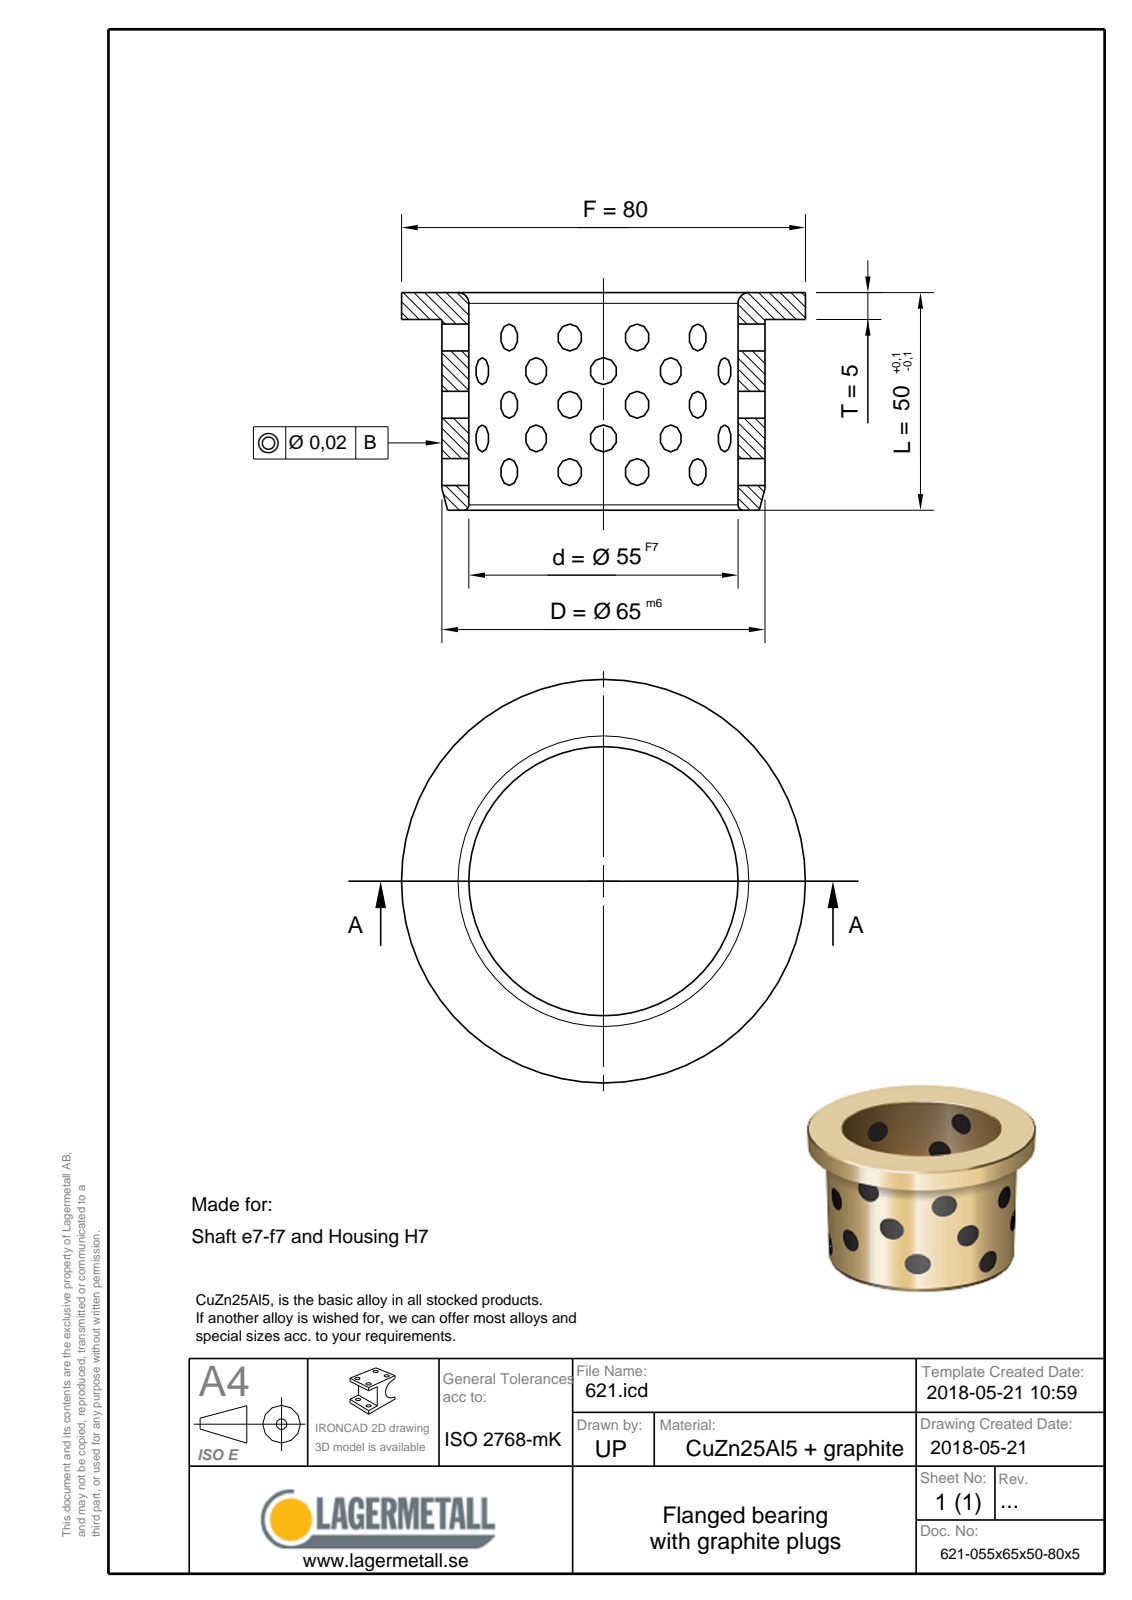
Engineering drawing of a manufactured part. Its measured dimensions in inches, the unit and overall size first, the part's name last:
Units: inches
Overall size (bounding box): 3.15 × 3.15 × 1.969
Round holes (diameter × count): ⌀2.165 ×1
Round bosses / shafts (diameter × count): ⌀3.15 ×1, ⌀2.559 ×1
Main face-to-face distances: 0.197, 1.772, 1.969
Volume: 3.364 in³ · Surface area: 37.13 in²
Bodies: 1 solid, 9 faces (3 planar, 3 cylindrical, 3 other)
Part name (STEP PRODUCT): 621-055x65x50-80x5
STEP written by: Spatial InterOp 3D (CONFIG_CONTROL_DESIGN)
